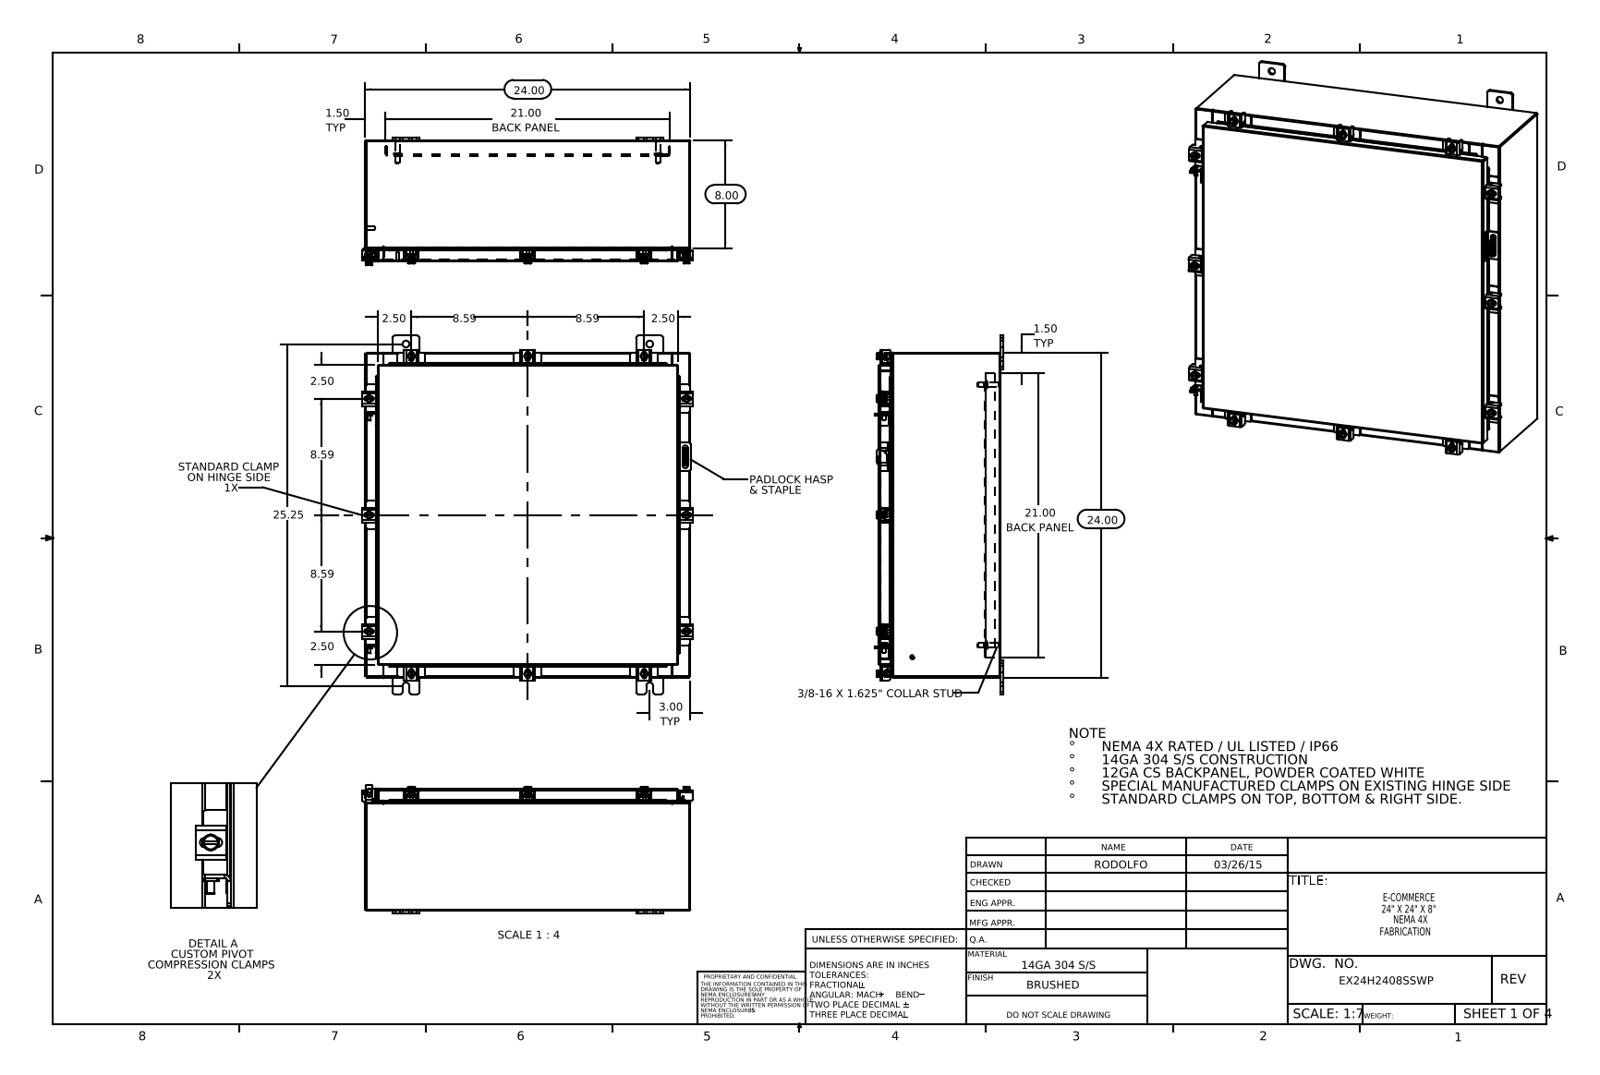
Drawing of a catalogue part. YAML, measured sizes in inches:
part_name: "EX24H2408SSWP Cover; EX24H2408SSWP Backpanel; 22104005_DEFAULT_RTP30; EX24H2408SSWP Bottom (+8 more)"
step_written_by: "SolidWorks 2014 (CONFIG_CONTROL_DESIGN)"
units: inches
bodies: {solids: 81, faces: 2018, planar: 1075, cylindrical: 783, other: 160}
overall_size: [26.5, 24.421, 9.453]
volume: 216.5
surface_area: 5406
round_holes:
  - {diameter: 0.213, count: 12}
  - {diameter: 0.26, count: 12}
  - {diameter: 0.5, count: 8}
  - {diameter: 0.125, count: 1}
  - {diameter: 0.25, count: 1}
round_bosses_or_shafts:
  - {diameter: 0.5, count: 12}
  - {diameter: 0.25, count: 12}
  - {diameter: 0.399, count: 10}
  - {diameter: 0.625, count: 4}
  - {diameter: 0.375, count: 4}
  - {diameter: 0.33, count: 4}
  - {diameter: 0.315, count: 2}
  - {diameter: 0.236, count: 2}
partial_cylinders:
  - {radius: 0.06, count: 54}
  - {radius: 0.013, count: 24}
  - {radius: 0.141, count: 24}
  - {radius: 0.19, count: 24}
  - {radius: 0.088, count: 22}
  - {radius: 0.12, count: 22}
  - {radius: 0.09, count: 18}
  - {radius: 0.05, count: 17}
face_to_face_distances: [0.075, 8.9, 23.925, 8.975, 8.826, 0.104, 1, 1.075, 7.826, 7.9]
hole_center_spacings: [20.559, 2.34, 18.34, 21.376, 23.451, 4.429, 8.593, 8.595]
